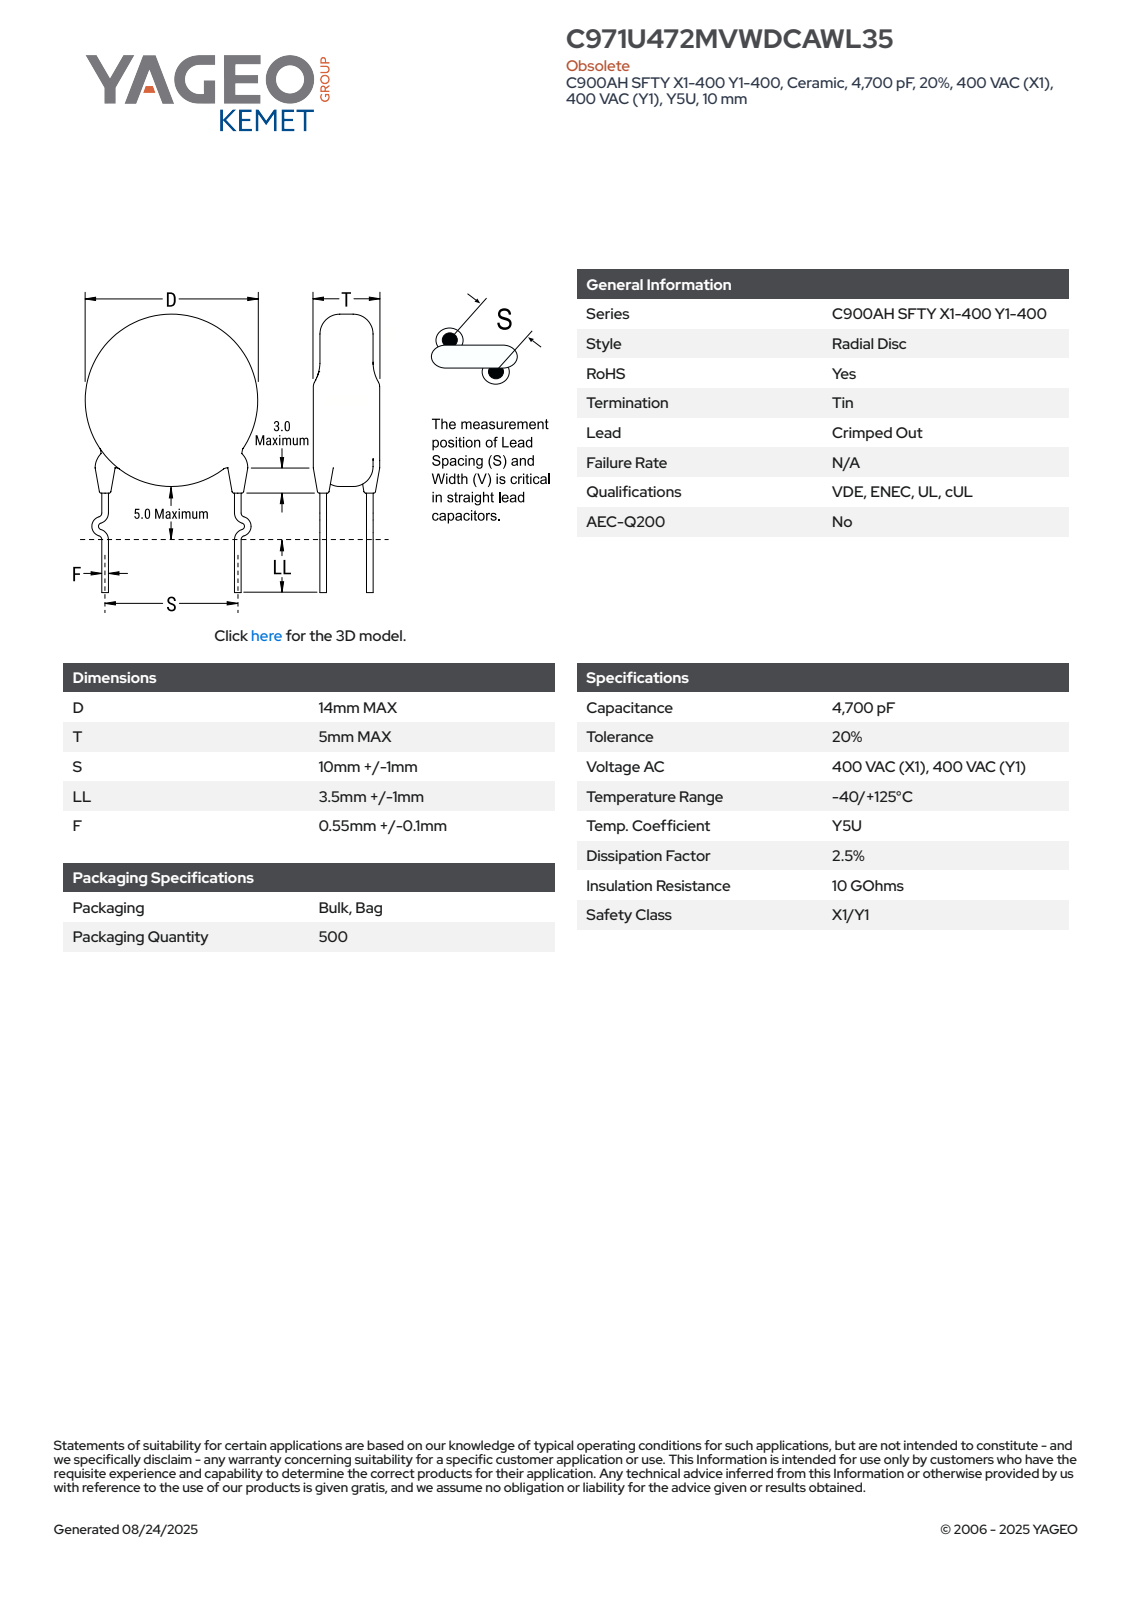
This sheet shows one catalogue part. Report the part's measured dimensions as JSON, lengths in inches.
{"part_name": "CCD_KCOC900_D14T5S10LL4.5F0.55", "step_written_by": "SolidWorks 2014 (AUTOMOTIVE_DESIGN)", "units": "inches", "bodies": {"solids": 4, "faces": 85, "planar": 63, "cylindrical": 6, "other": 16}, "overall_size": [0.925, 0.596, 0.197], "volume_in3": 0.047, "surface_area_in2": 0.876, "round_bosses_or_shafts": [[0.047, 2], [0.551, 1]], "face_to_face_distances": [0.197, 0.305, 0.248, 0.057, 0.016, 0.234, 0.035, 0.046, 0.17, 0.176]}
